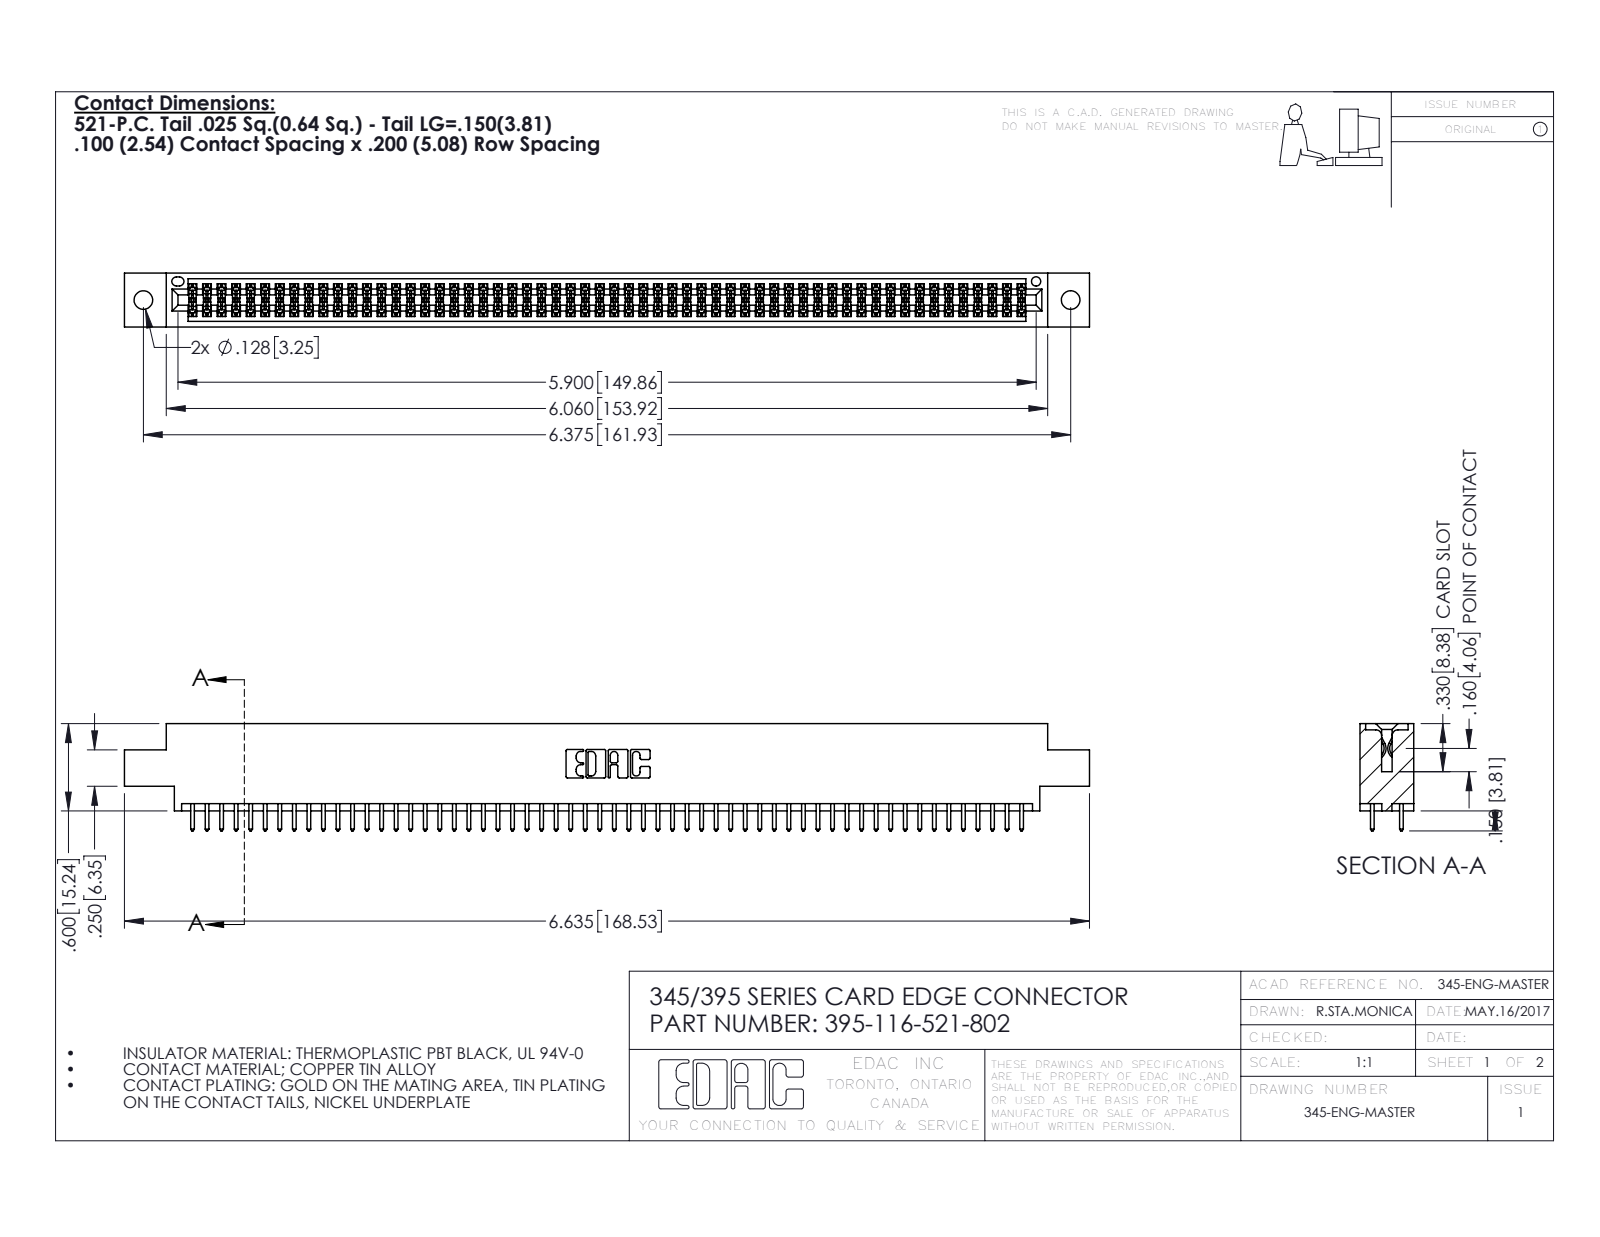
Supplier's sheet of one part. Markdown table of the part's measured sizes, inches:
| quantity | value |
| --- | --- |
| part name | 395-116-521-802; 345 Part_0.170 Offset - 0.128 Dia; 345-292-001_345-293-121 |
| STEP written by | SolidWorks 2016 (CONFIG_CONTROL_DESIGN) |
| units | inches |
| bodies | 117 solids, 5930 faces (3912 planar, 2018 cylindrical, 0 other) |
| overall size | 6.635 × 0.737 × 0.37 |
| volume | 0.996 in³ |
| surface area | 37.2 in² |
| round holes (diameter × count) | 0.128 × 2, 0.064 × 1 |
| partial cylindrical surfaces (radius × count) | 0.006 × 174, 0.01 × 116, 0.01 × 22, 0.007 × 6, 0.031 × 6, 0.026 × 3, 0.014 × 2, 0.019 × 2 |
| main face-to-face distances | 0.298, 0.072, 0.2, 0.37, 0.098, 0.272, 0.025, 0.225, 0.175, 0.149 |
| hole center spacings | 0.27, 6.139, 6.375 |
